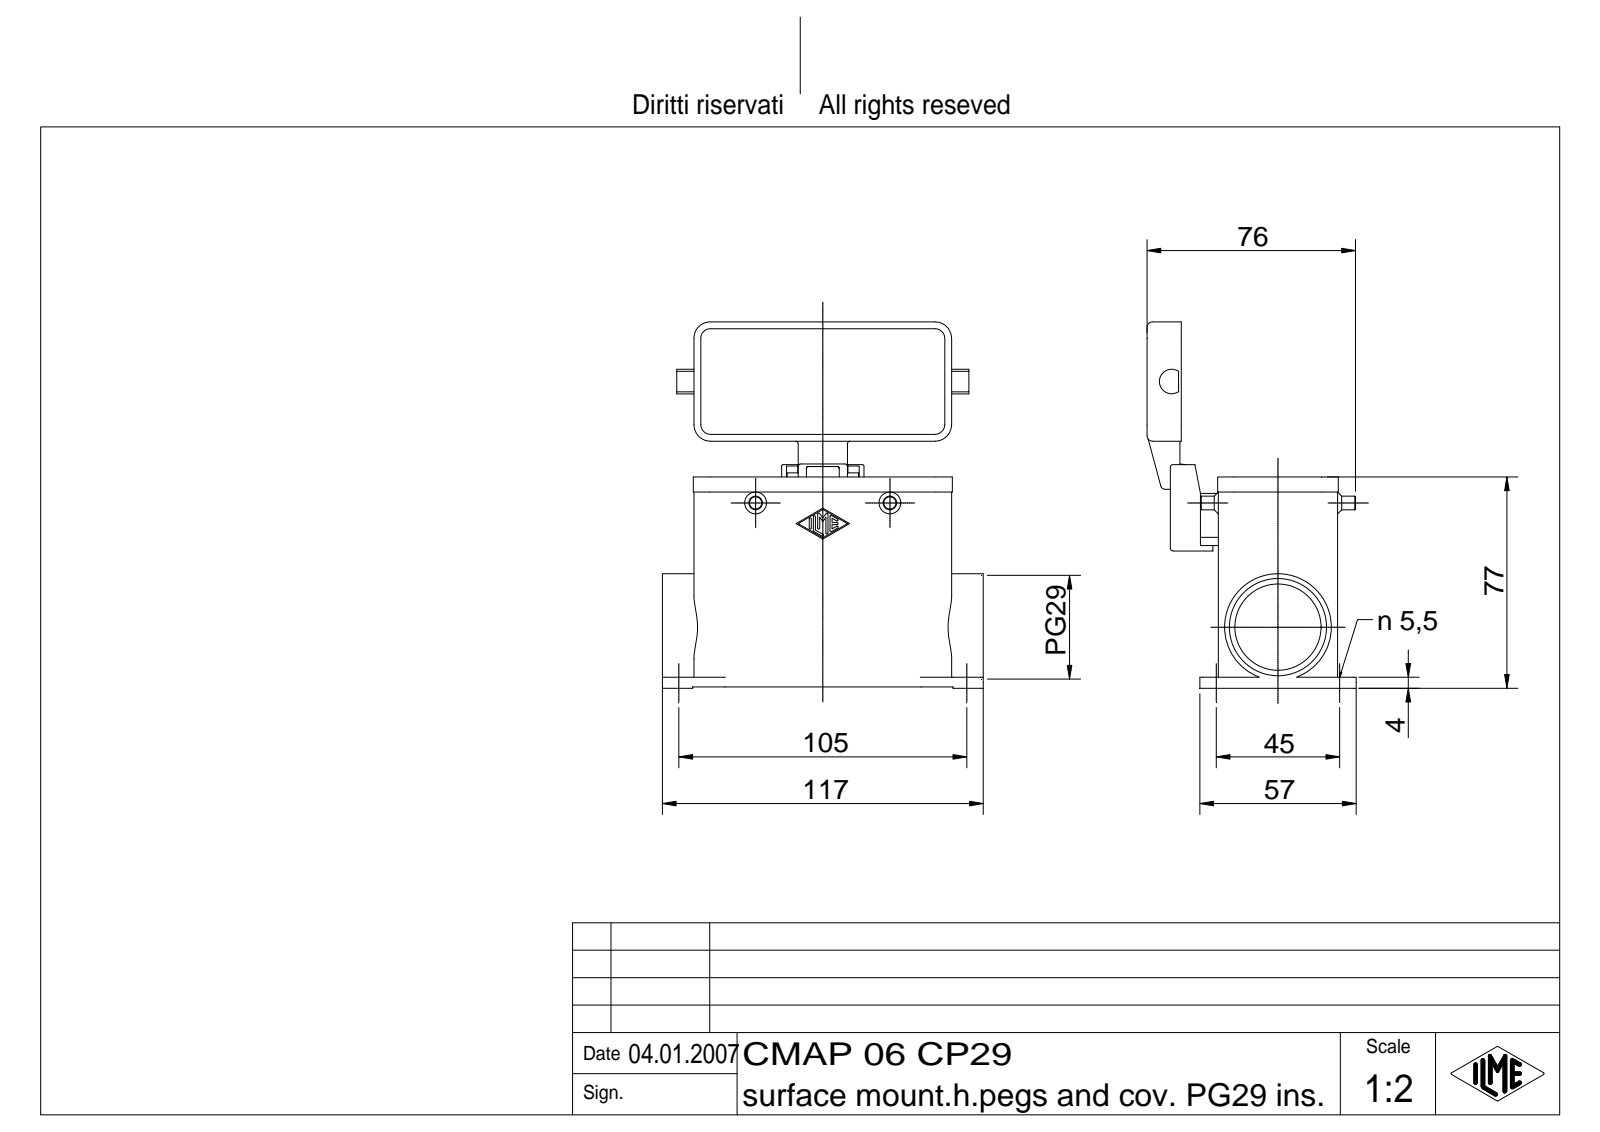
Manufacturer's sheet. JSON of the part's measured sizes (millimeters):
{"part_name": "CMAP 06 CP29", "step_written_by": "Autodesk Inventor 7 (AUTOMOTIVE_DESIGN)", "units": "millimeters", "bodies": {"solids": 2, "faces": 475, "planar": 175, "cylindrical": 179, "other": 121}, "overall_size": [133.5, 117, 76.25], "volume_mm3": 129031, "surface_area_mm2": 74469, "round_holes": [[5.5, 4], [4, 1], [5, 1], [31.48, 1], [35.48, 1]], "round_bosses_or_shafts": [[5, 2], [3, 2], [38.98, 1], [7, 1], [4, 1]], "partial_cylinders_radius": [[1, 26], [0.38, 14], [6, 12], [0.5, 9], [0.7, 8], [2, 8], [3, 4], [3.5, 4]], "face_to_face_distances": [3, 40.5, 3.5, 43.5, 37.5, 29, 22.5, 69.5, 66.5, 26], "hole_center_spacings": [45, 105, 114.24]}
